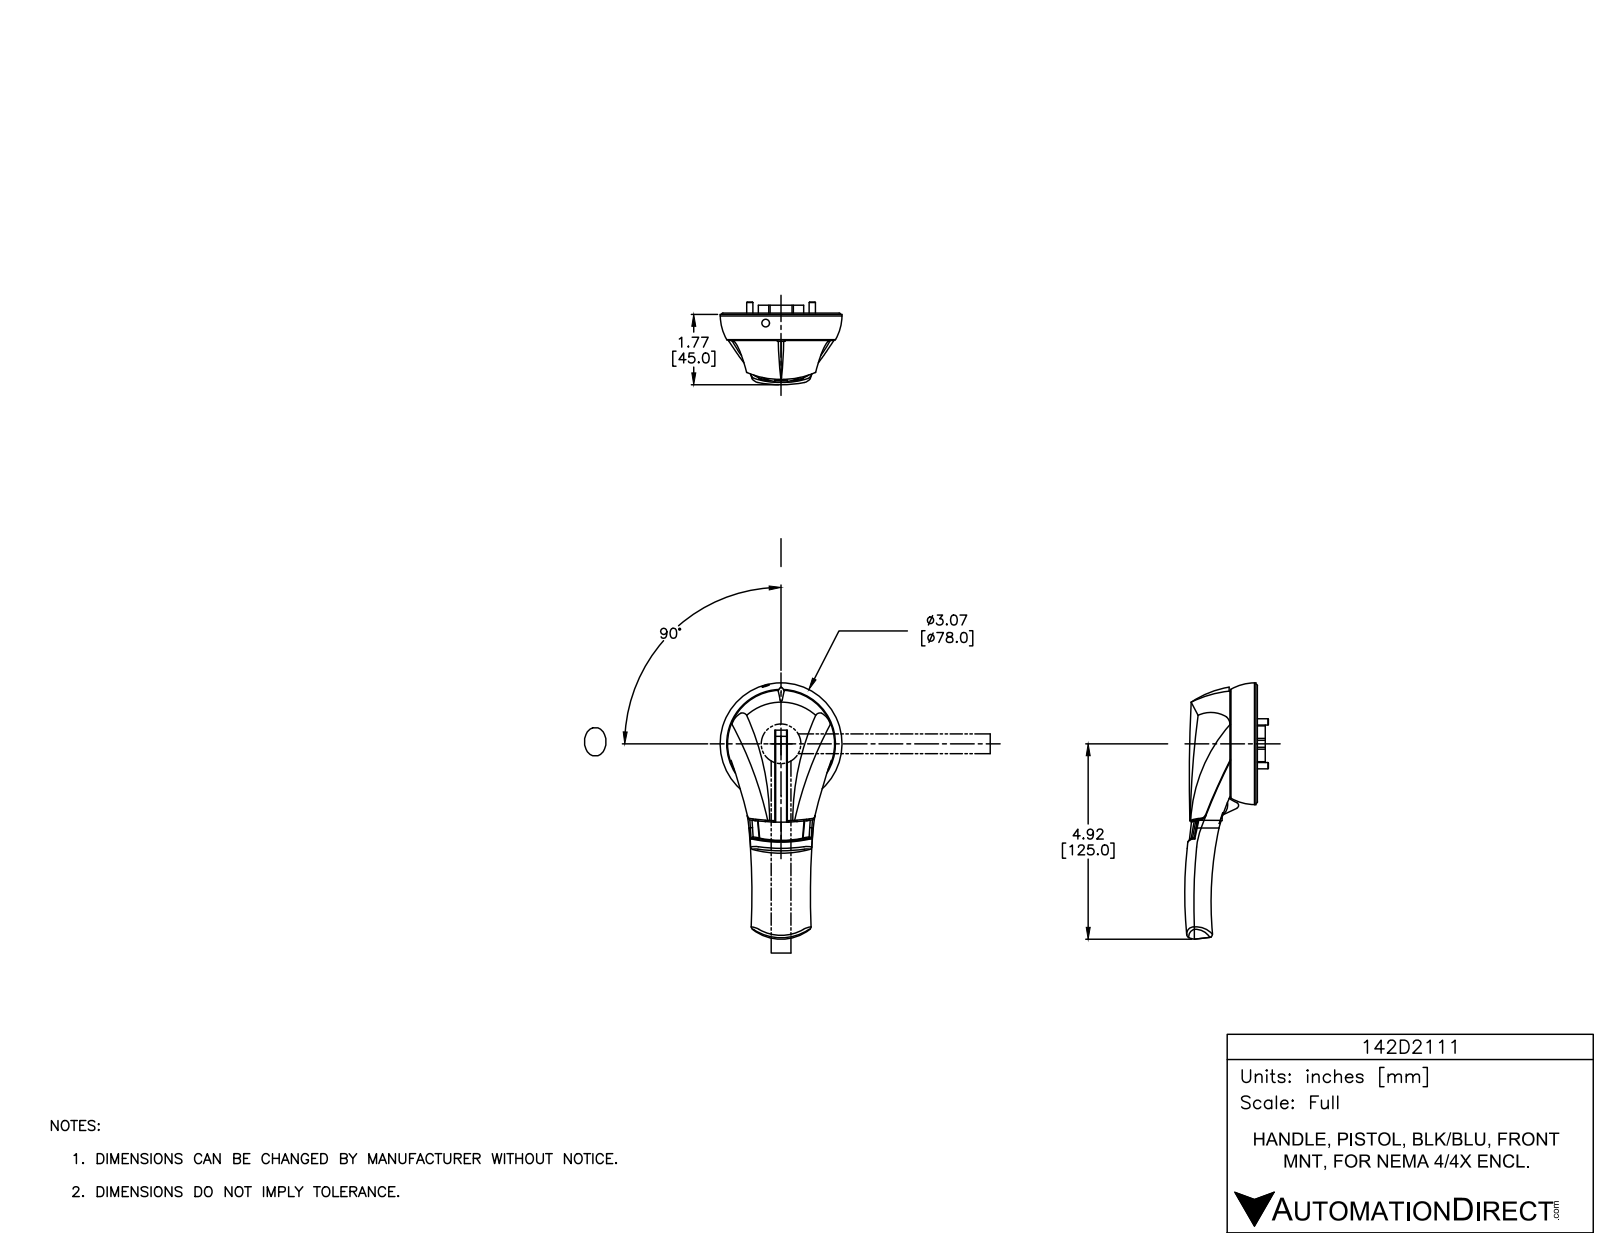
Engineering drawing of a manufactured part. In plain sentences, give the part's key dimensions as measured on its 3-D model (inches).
The part is named "142D2111". Its 3-D file was written by "SolidWorks 2015 (AUTOMOTIVE_DESIGN)". It is 8 solids with 1516 faces: 810 planar, 548 cylindrical and 158 other. Overall it measures 6.458 by 3.07 by 2.079 inches. Its volume is 9.514 cubic inches and its surface area 87.32 square inches. Round holes: 6 of diameter 0.157, 4 of diameter 0.339, 4 of diameter 0.425, 3 of diameter 0.03, 2 of diameter 0.169, 2 of diameter 0.362, 1 of diameter 0.118, 1 of diameter 0.189, 1 of diameter 2.992. Round bosses or shafts: 11 of diameter 0.02, 4 of diameter 0.335, 4 of diameter 0.315, 3 of diameter 0.089, 3 of diameter 0.069, 2 of diameter 0.228, 1 of diameter 2.819, 1 of diameter 2.701. Partial cylindrical surfaces (rounded edges, fillets, slot ends): 221 of radius 0.01, 20 of radius 0.015, 20 of radius 0.034, 15 of radius 0.03, 4 of radius 0.039, 3 of radius 0.025, 3 of radius 5.437, 2 of radius 0.079. The main face-to-face distances are 0.024, 0.701, 0.713, 0.689, 0.035, 0.102, 0.276, 0.173, 0.244, 0.047. The hole center spacings are 0.961, 0.309, 0.669, 1.098, 1.102, 1.203, 1.575, 1.881.
